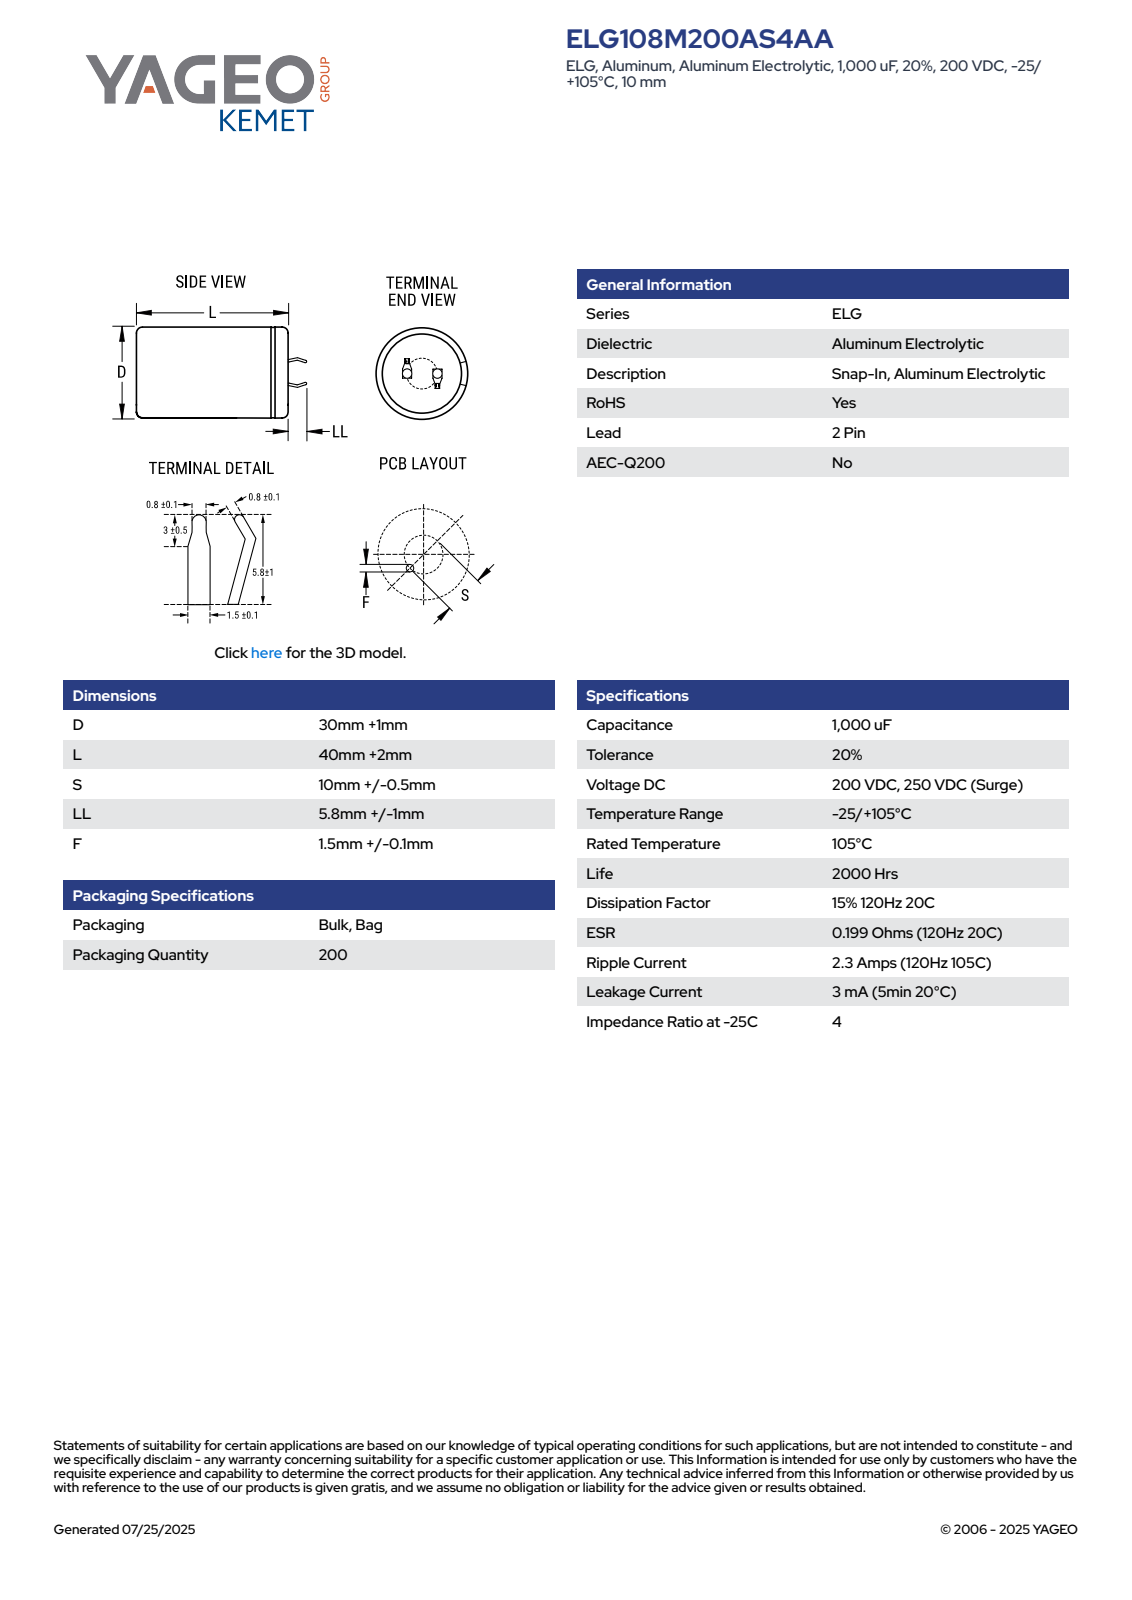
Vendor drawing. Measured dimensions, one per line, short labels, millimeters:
name: CARS_K2P_30X40_D31L42S10LL6.8F1.6
written by: SolidWorks 2014 (AUTOMOTIVE_DESIGN)
unit: mm
bodies: 1 solid, 100 faces (52 planar, 9 cylindrical, 39 other)
size: 48.79 × 31 × 31
volume: 31 366 mm³; area: 5 608 mm²
holes: 1× ⌀27.43
bosses: 1× ⌀31
rounds: 1× R15.49
face distances: 41.99, 0.6, 42.49, 0.5, 7.08, 7.63, 0.75, 1.35, 7.68, 6.48
